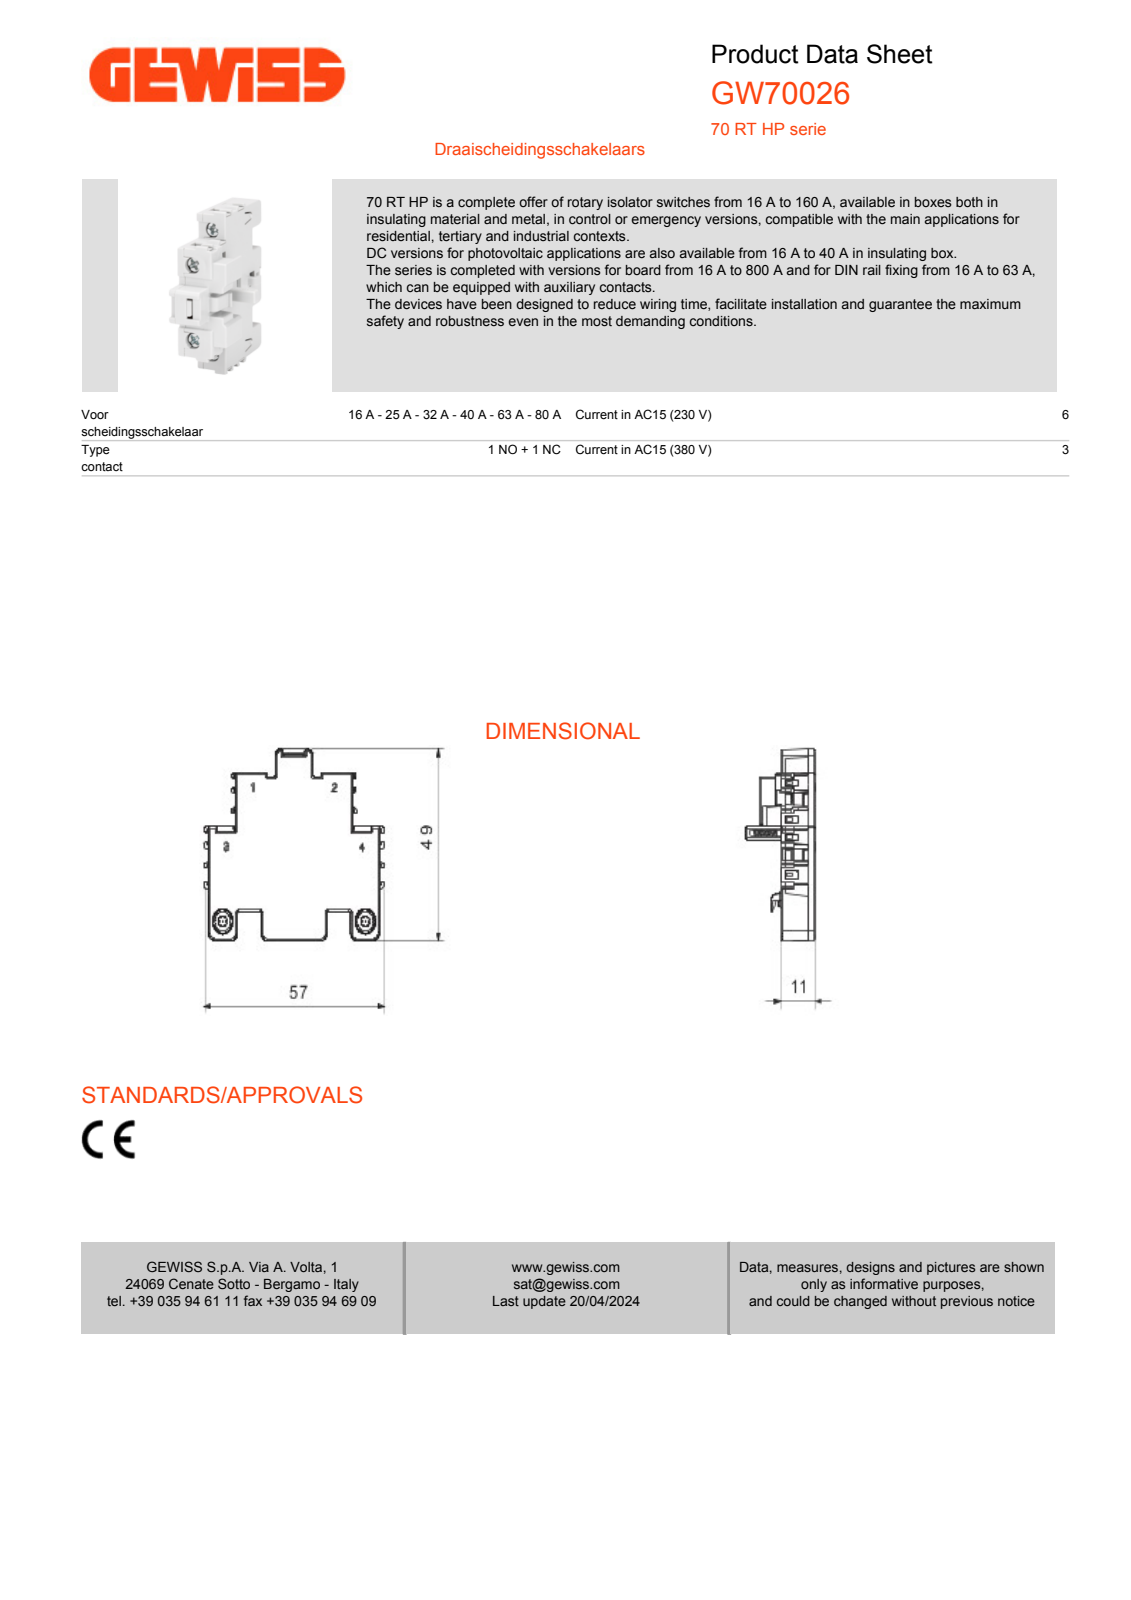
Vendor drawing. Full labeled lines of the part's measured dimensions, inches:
Part name (STEP PRODUCT): COPERCHIO_AUS_SEZ; FONDO_CONTATTO_AUSILIARIO; GW70026_ASM
STEP written by: CREO PARAMETRIC BY PTC INC, 2020354 (CONFIG_CONTROL_DESIGN)
Units: inches
Bodies: 2 solids, 888 faces (787 planar, 73 cylindrical, 28 other)
Overall size (bounding box): 2.255 × 1.929 × 0.691
Volume: 0.647 in³ · Surface area: 27.13 in²
Round holes (diameter × count): ⌀0.106 ×2, ⌀0.13 ×2
Partial cylindrical surfaces — rounded edges, fillets, slot ends (radius × count): R0.008 ×10, R0.079 ×10, R0.059 ×6, R0.01 ×4, R0.071 ×4, R0.104 ×4, R0.108 ×4, R0.02 ×2
Main face-to-face distances: 0.059, 0.051, 0.382, 0.433, 0.323, 0.374, 0.039, 0.283, 0.343, 0.091
Hole centre spacings: 1.791
